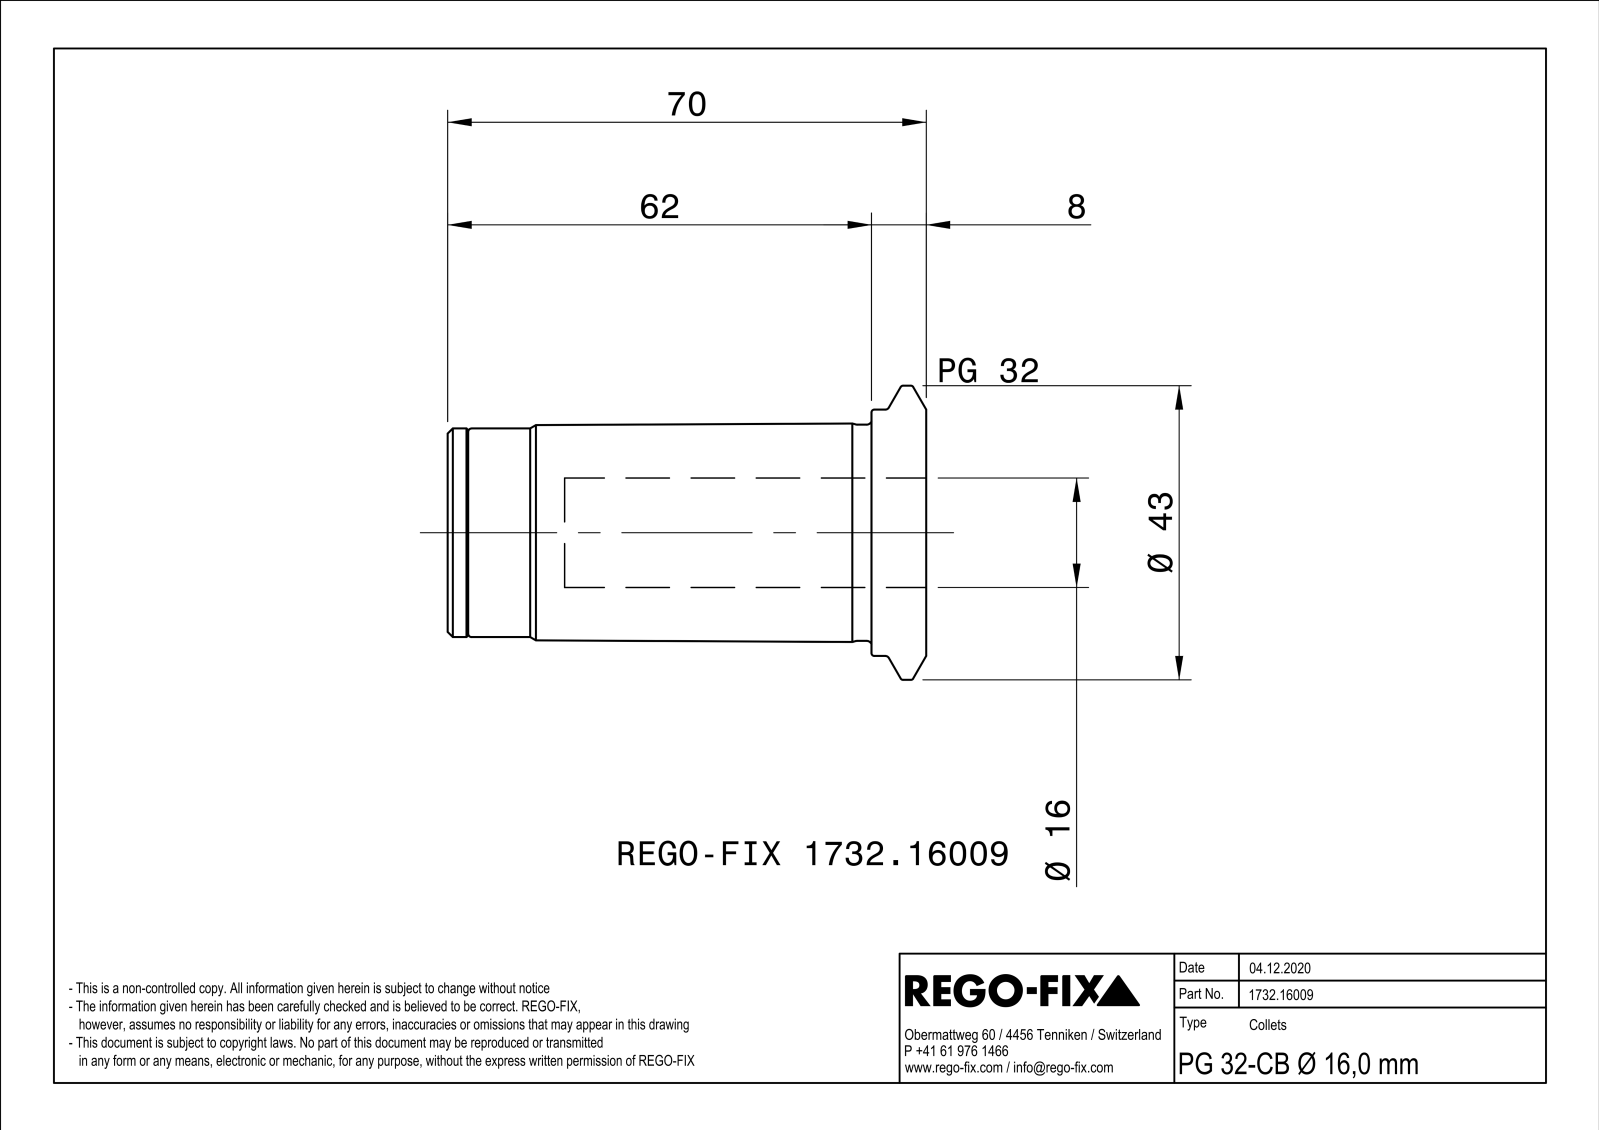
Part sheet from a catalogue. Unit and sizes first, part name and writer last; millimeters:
Units: millimetres
Overall size (bounding box): 70 × 43 × 42.99
Round holes (diameter × count): ⌀1.5 ×3, ⌀4 ×3, ⌀8.92 ×1, ⌀10.5 ×1, ⌀16 ×1, ⌀26.92 ×1, ⌀28.5 ×1
Round bosses / shafts (diameter × count): ⌀43 ×1, ⌀36 ×1, ⌀31.6 ×1, ⌀30.5 ×1, ⌀28 ×1, ⌀26.5 ×1, ⌀21 ×1
Partial cylindrical surfaces — rounded edges, fillets, slot ends (radius × count): R2 ×6, R1.5 ×3, R3.5 ×3, R3.98 ×1, R4.75 ×1, R8.75 ×1
Main face-to-face distances: 1, 70, 8, 59, 67, 3, 58, 9, 12, 11
Hole centre spacings: 7.75, 9.25, 12.02, 4.7, 13.42, 16.03, 16.44, 4.69
Volume: 5 840 mm³ · Surface area: 18 639 mm²
Bodies: 1 solid, 136 faces (29 planar, 46 cylindrical, 61 other)
Part name (STEP PRODUCT): NOCUT
STEP written by: SIEMENS PLM Software Solid Edge ST10 (AUTOMOTIVE_DESIGN)
